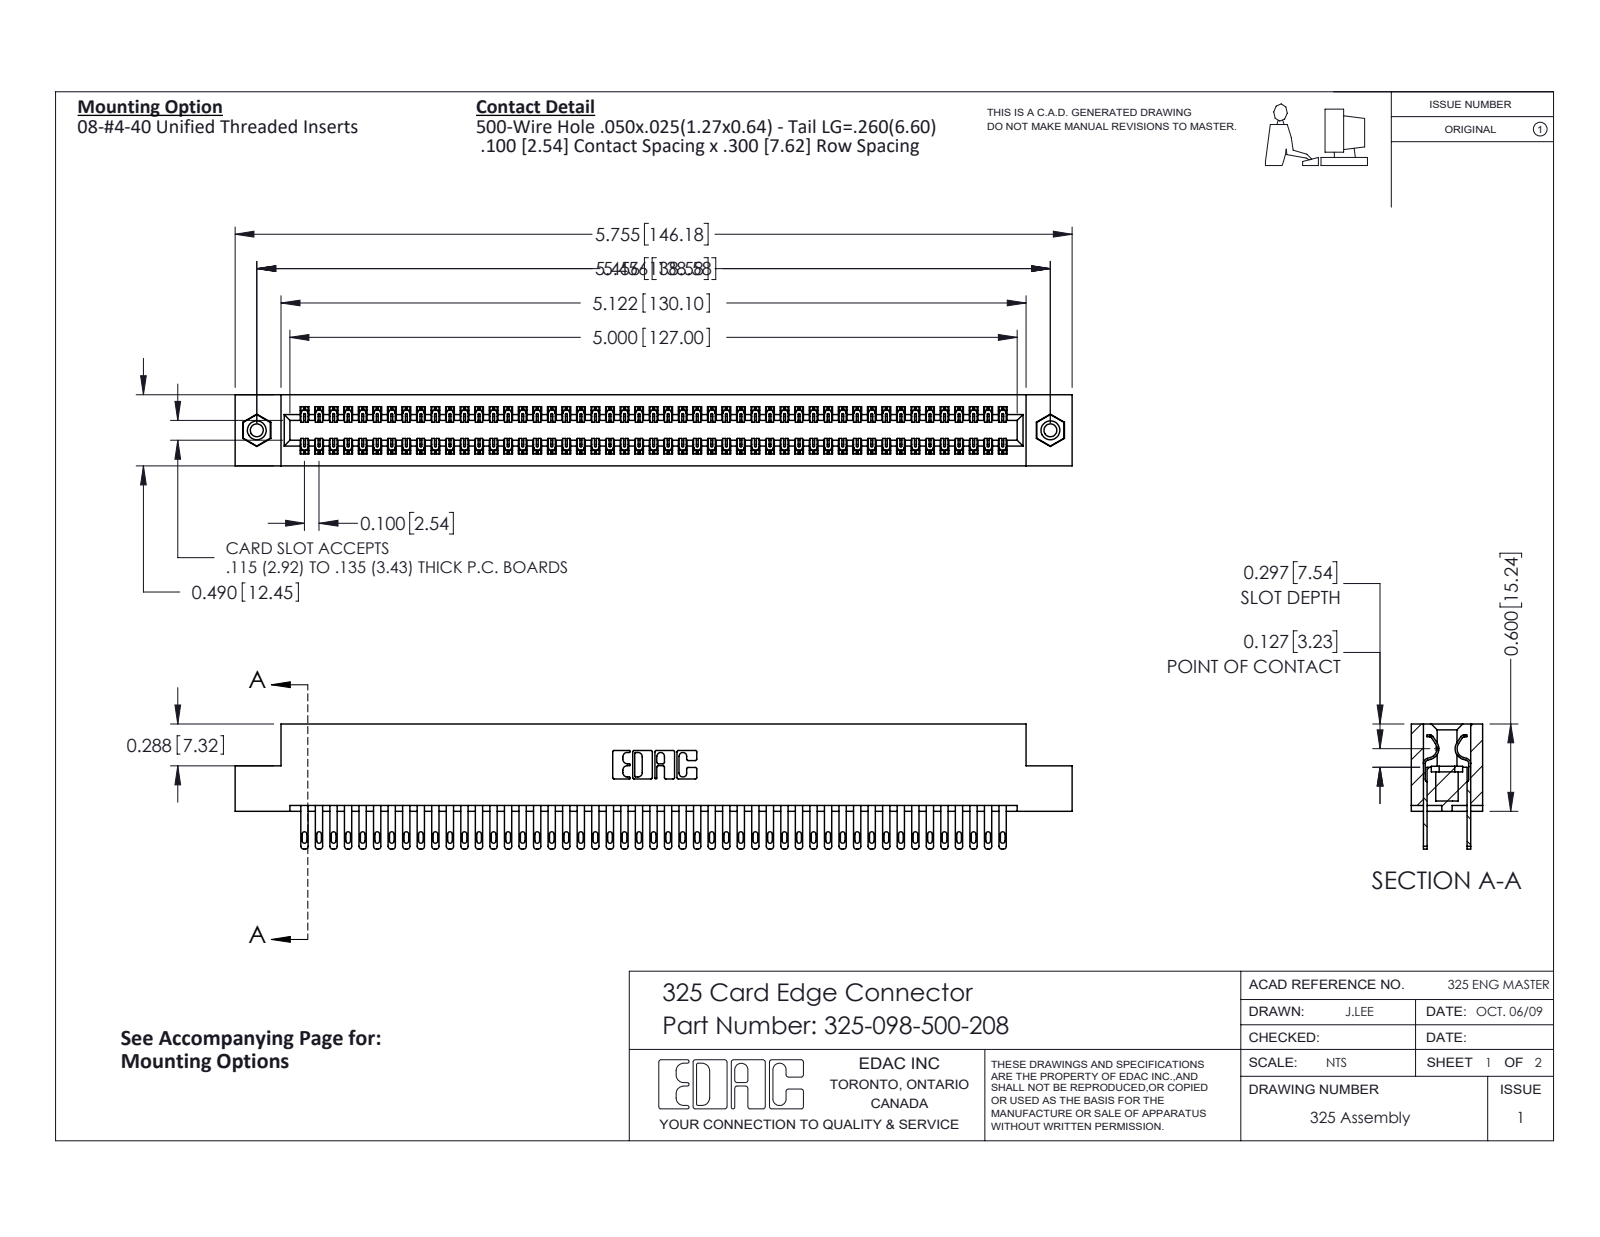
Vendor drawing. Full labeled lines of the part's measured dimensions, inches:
Part name (STEP PRODUCT): 345-250-001_345-250-003-102; 325-292-001_325-293-100; 325 Part_TI; 325-098-500-208
STEP written by: SolidWorks 2016 (CONFIG_CONTROL_DESIGN)
Units: inches
Bodies: 101 solids, 4878 faces (3042 planar, 1820 cylindrical, 16 other)
Overall size (bounding box): 5.755 × 0.86 × 0.49
Volume: 1.173 in³ · Surface area: 37.94 in²
Round holes (diameter × count): ⌀0.089 ×2, ⌀0.125 ×2, ⌀0.16 ×2
Round bosses / shafts (diameter × count): ⌀0.155 ×2
Partial cylindrical surfaces — rounded edges, fillets, slot ends (radius × count): R0.006 ×147, R0.016 ×98, R0.02 ×98, R0.01 ×22, R0.007 ×6, R0.031 ×6, R0.026 ×3, R0.014 ×2
Main face-to-face distances: 0.083, 0.407, 0.3, 0.107, 0.383, 0.025, 0.49, 0.325, 0.275, 0.56
Hole centre spacings: 5.456
